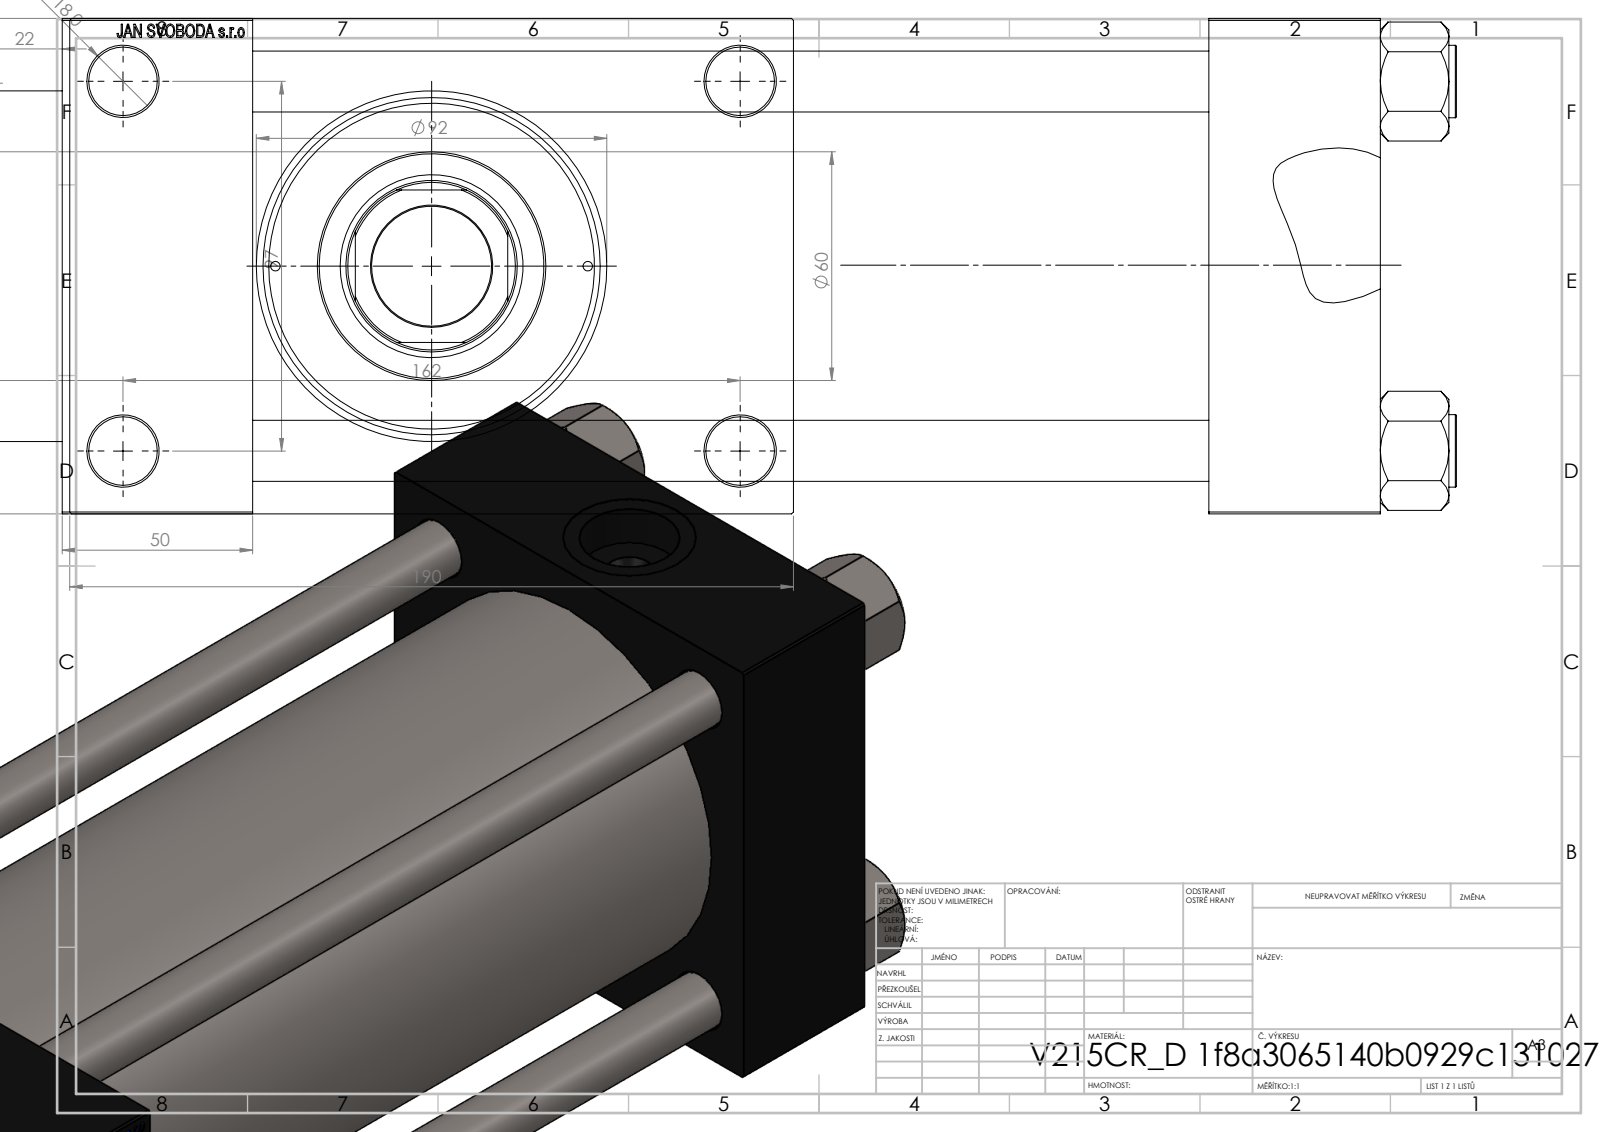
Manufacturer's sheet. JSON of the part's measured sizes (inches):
{"part_name": "V215CR_VCP_D; V215_VC_A; NUT_M5_D; V215CR_D_Body (+1 more)", "step_written_by": "SolidWorks 2019 (CONFIG_CONTROL_DESIGN)", "units": "inches", "bodies": {"solids": 11, "faces": 1160, "planar": 547, "cylindrical": 93, "other": 520}, "overall_size": [16.654, 7.48, 5.118], "volume_in3": 196, "surface_area_in2": 822.1, "round_holes": [[0.63, 4], [0.709, 4], [0.098, 2], [0.276, 2], [1.041, 2], [1.378, 2], [1.24, 1], [1.772, 1], [1.89, 1], [2.992, 1], [3.366, 1], [3.937, 1]], "round_bosses_or_shafts": [[0.748, 4], [4.173, 1], [3.622, 1], [2.362, 1]], "partial_cylinders_radius": [[0.866, 1]], "face_to_face_distances": [5.118, 1.772, 11.654, 9.882, 13.622, 11.85, 1.969, 1.181, 6.299, 7.48], "hole_center_spacings": [1.281, 1.93, 2.475, 2.698, 3.717, 3.815, 4.005, 4.026]}
